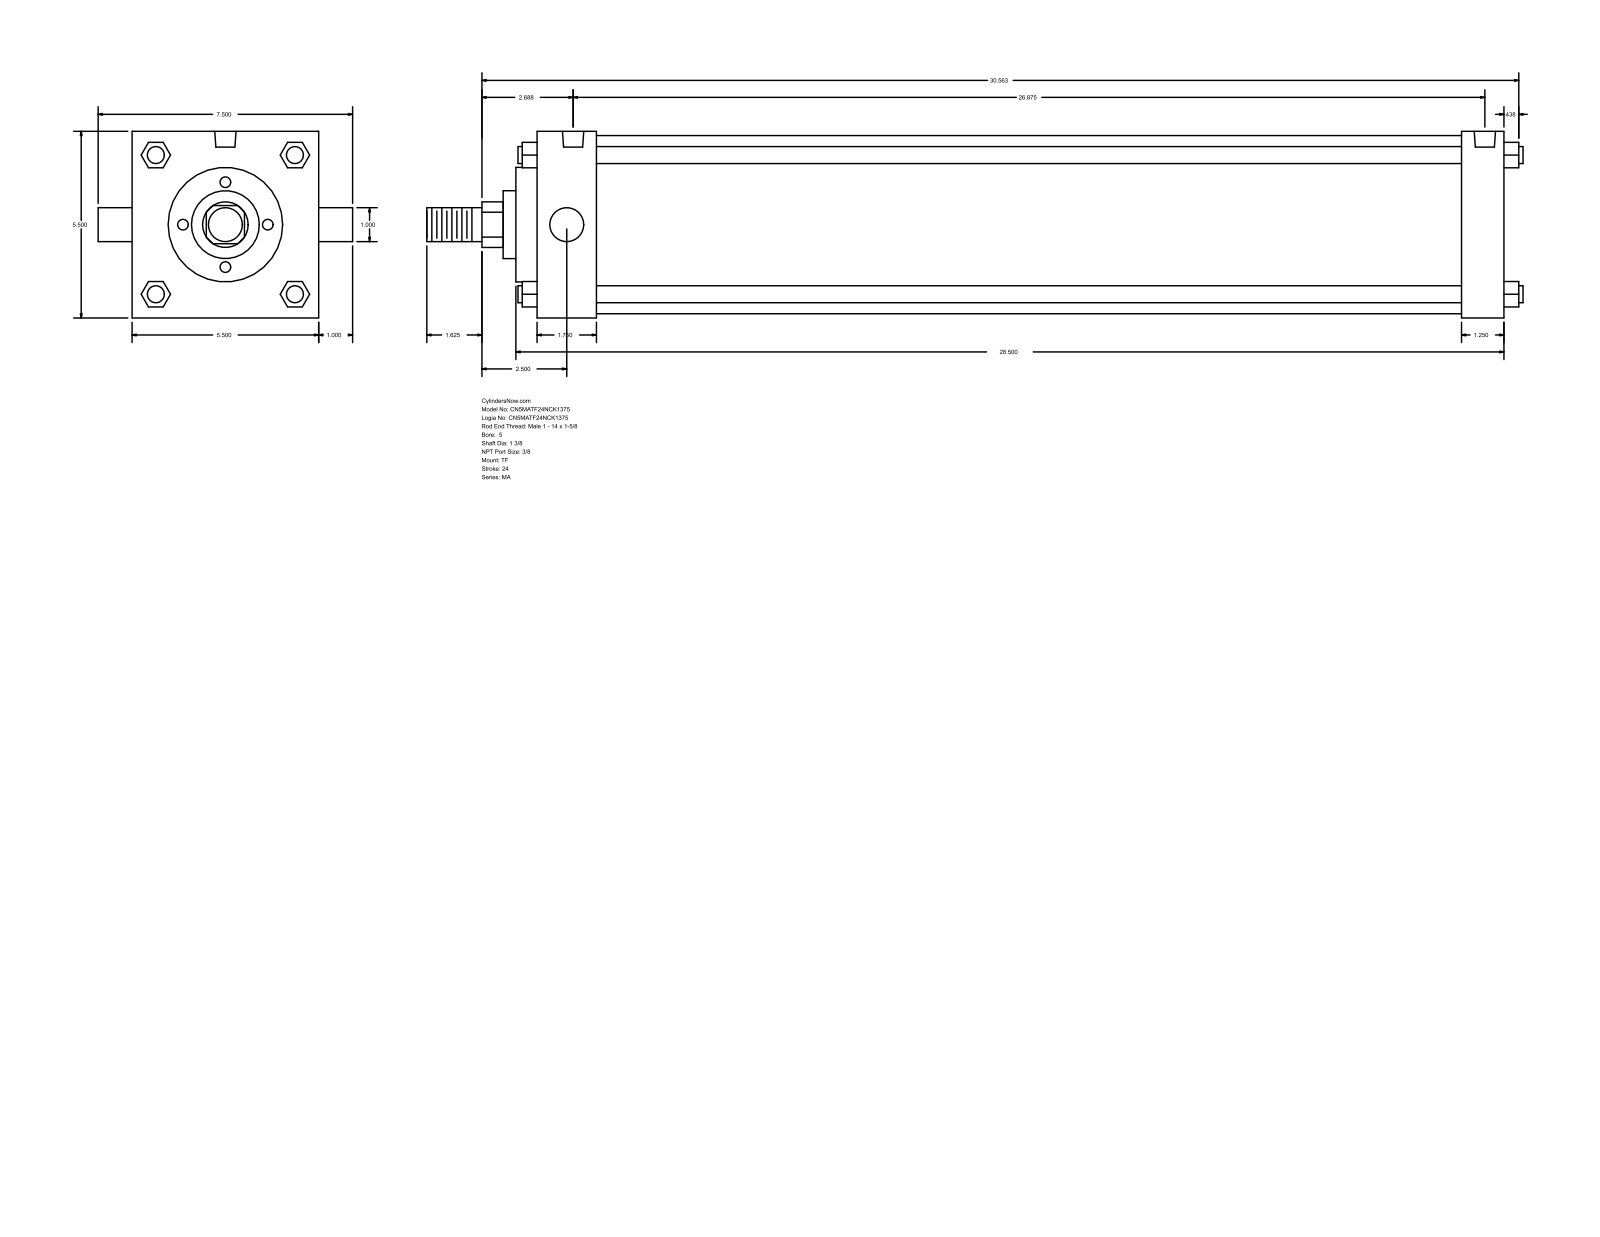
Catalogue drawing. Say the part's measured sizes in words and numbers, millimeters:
The part is named "MA_TF__0500_1.375". Its 3-D file was written by "GSSL Pune (CONFIG_CONTROL_DESIGN)". It is 0 solids with 122 faces: 93 planar, 29 cylindrical and 0 other. Overall it measures 820.74 by 190.5 by 139.7 millimeters. Round holes: 3 of diameter 11.11, 2 of diameter 15.93. Round bosses or shafts: 4 of diameter 12.7, 2 of diameter 25.4, 1 of diameter 133.35, 1 of diameter 85.72, 1 of diameter 50.8, 1 of diameter 34.92. Partial cylindrical surfaces (rounded edges, fillets, slot ends): 1 of radius 17.06. The main face-to-face distances are 139.7, 723.9, 692.15, 31.75, 44.45, 647.7, 679.45, 15.87, 60.32, 708.02. The hole center spacings are 4.77, 677.86, 673.09, 682.63.
